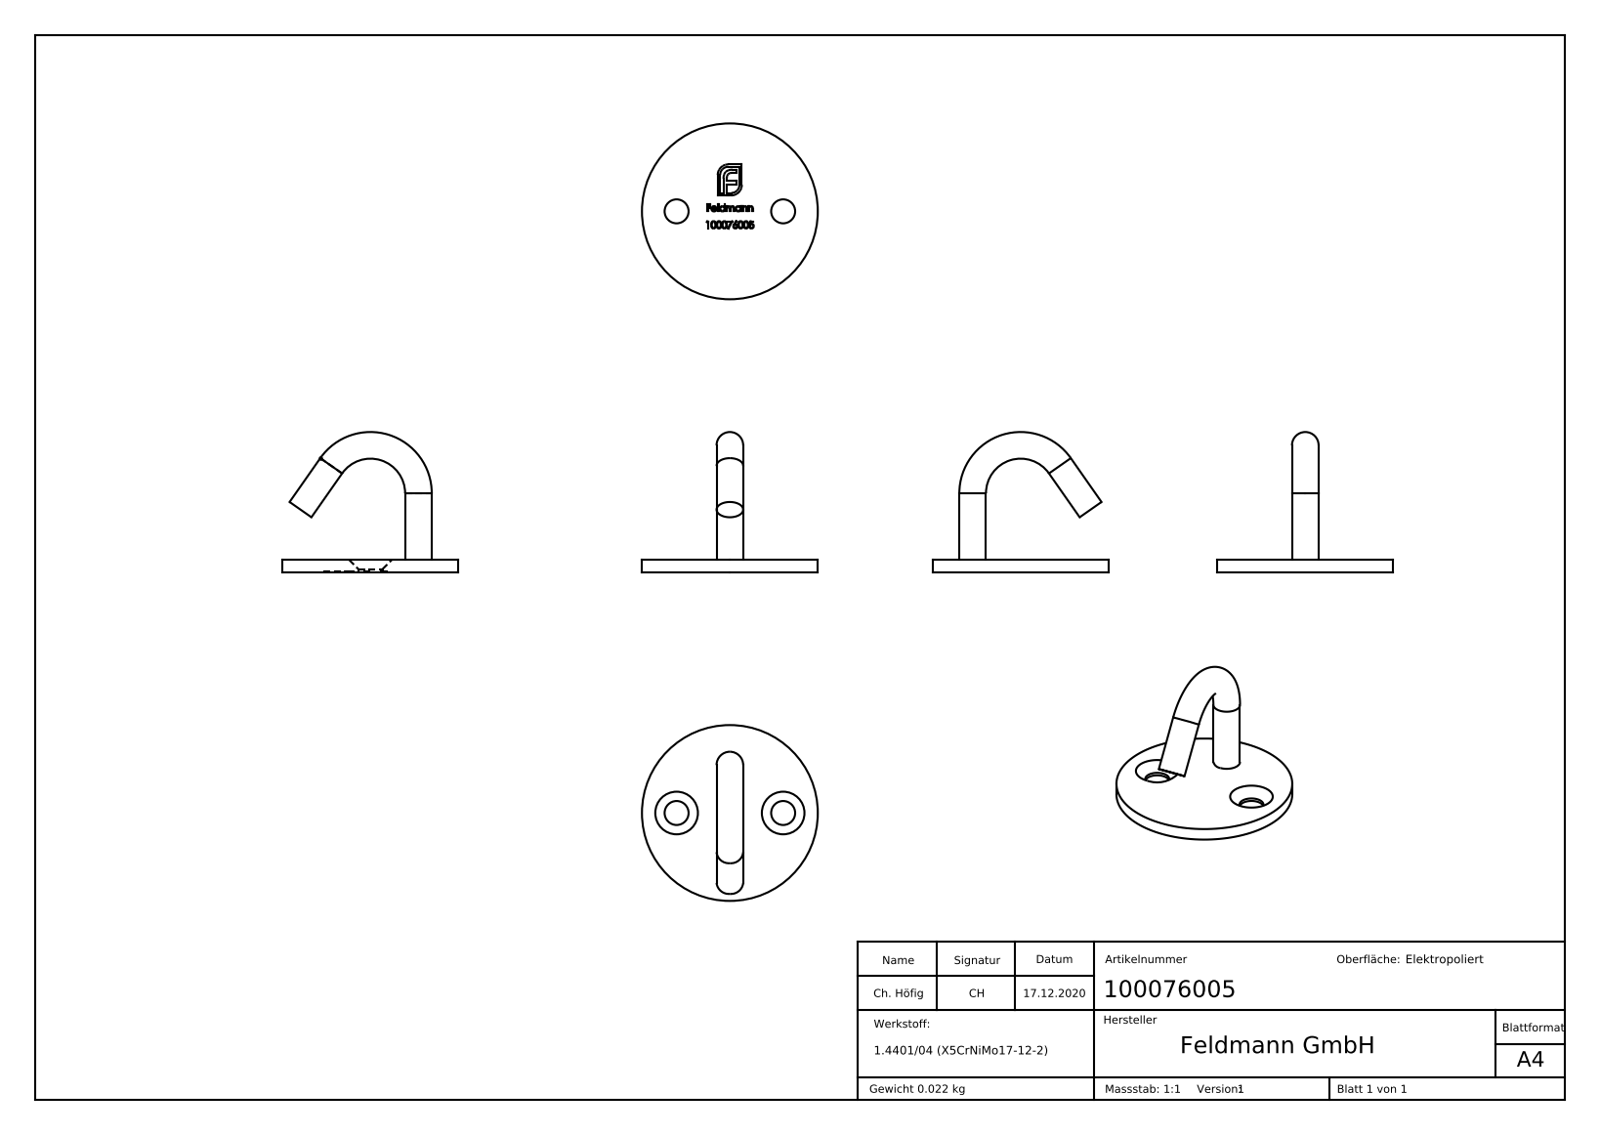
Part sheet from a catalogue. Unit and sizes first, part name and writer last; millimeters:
Units: millimetres
Overall size (bounding box): 33 × 33 × 26.3
Round holes (diameter × count): ⌀4.5 ×2
Round bosses / shafts (diameter × count): ⌀5 ×2, ⌀33 ×1
Main face-to-face distances: 2.3, 2.2, 0.46, 5.35, 4.52, 3.11, 2.99, 1.25, 4.07, 0.45
Hole centre spacings: 20
Volume: 2 728 mm³ · Surface area: 2 656 mm²
Bodies: 1 solid, 271 faces (125 planar, 10 cylindrical, 136 other)
Part name (STEP PRODUCT): 100076005
STEP written by: SolidWorks 2018 (CONFIG_CONTROL_DESIGN)
